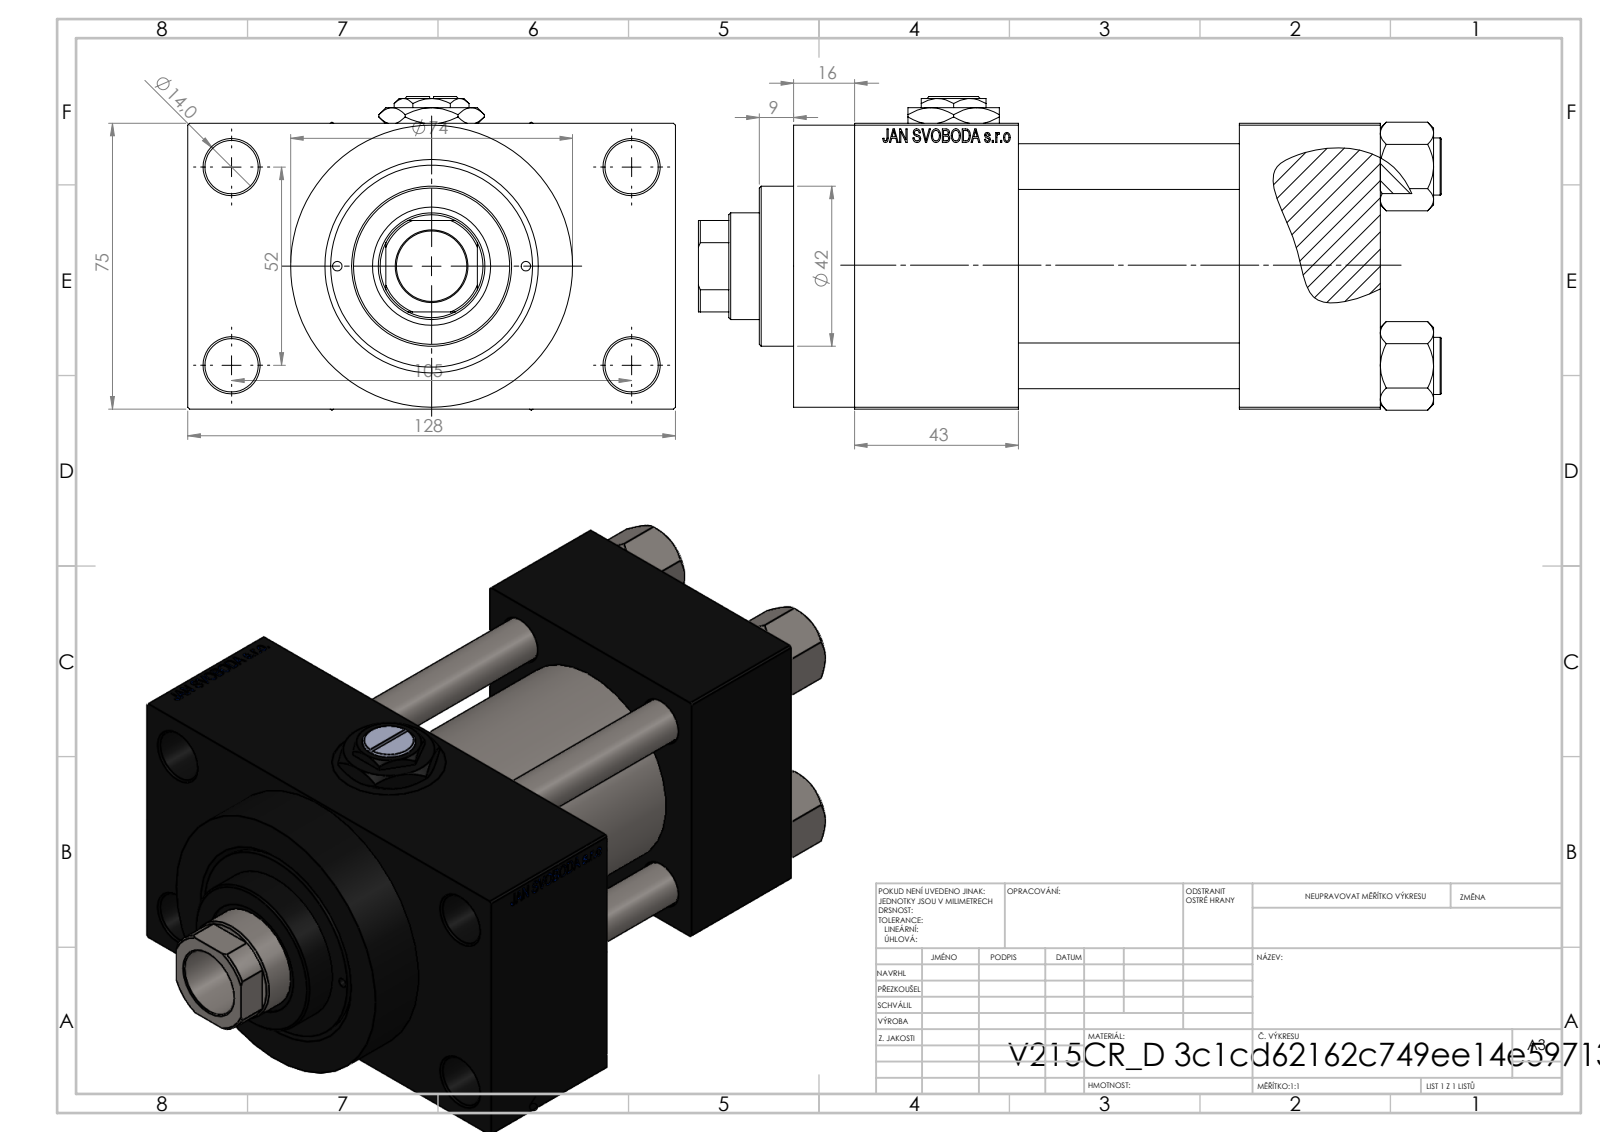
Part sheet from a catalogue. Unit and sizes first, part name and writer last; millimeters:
Units: millimetres
Overall size (bounding box): 195 × 128 × 82.27
Round holes (diameter × count): ⌀12 ×4, ⌀14 ×4, ⌀20.96 ×3, ⌀30 ×3, ⌀2.5 ×2, ⌀7 ×2, ⌀18.5 ×1, ⌀28 ×1, ⌀31 ×1, ⌀41 ×1, ⌀50 ×1, ⌀53 ×1
Round bosses / shafts (diameter × count): ⌀15 ×4, ⌀74 ×1, ⌀56 ×1, ⌀42 ×1
Partial cylindrical surfaces — rounded edges, fillets, slot ends (radius × count): R13.5 ×1
Main face-to-face distances: 75, 58, 37, 95, 26.5, 138, 101, 43, 101.5, 16
Hole centre spacings: 26.19, 26.35, 36.98, 38.03, 52.3, 57.22, 58.43, 58.59
Volume: 803 755 mm³ · Surface area: 172 171 mm²
Bodies: 12 solids, 1159 faces (523 planar, 96 cylindrical, 540 other)
Part name (STEP PRODUCT): V215CR_D_TYCINKA; V215_VC_A; V215CR_D_Body; Zatka_pro_OIL_PORT (+2 more)
STEP written by: SolidWorks 2019 (CONFIG_CONTROL_DESIGN)
